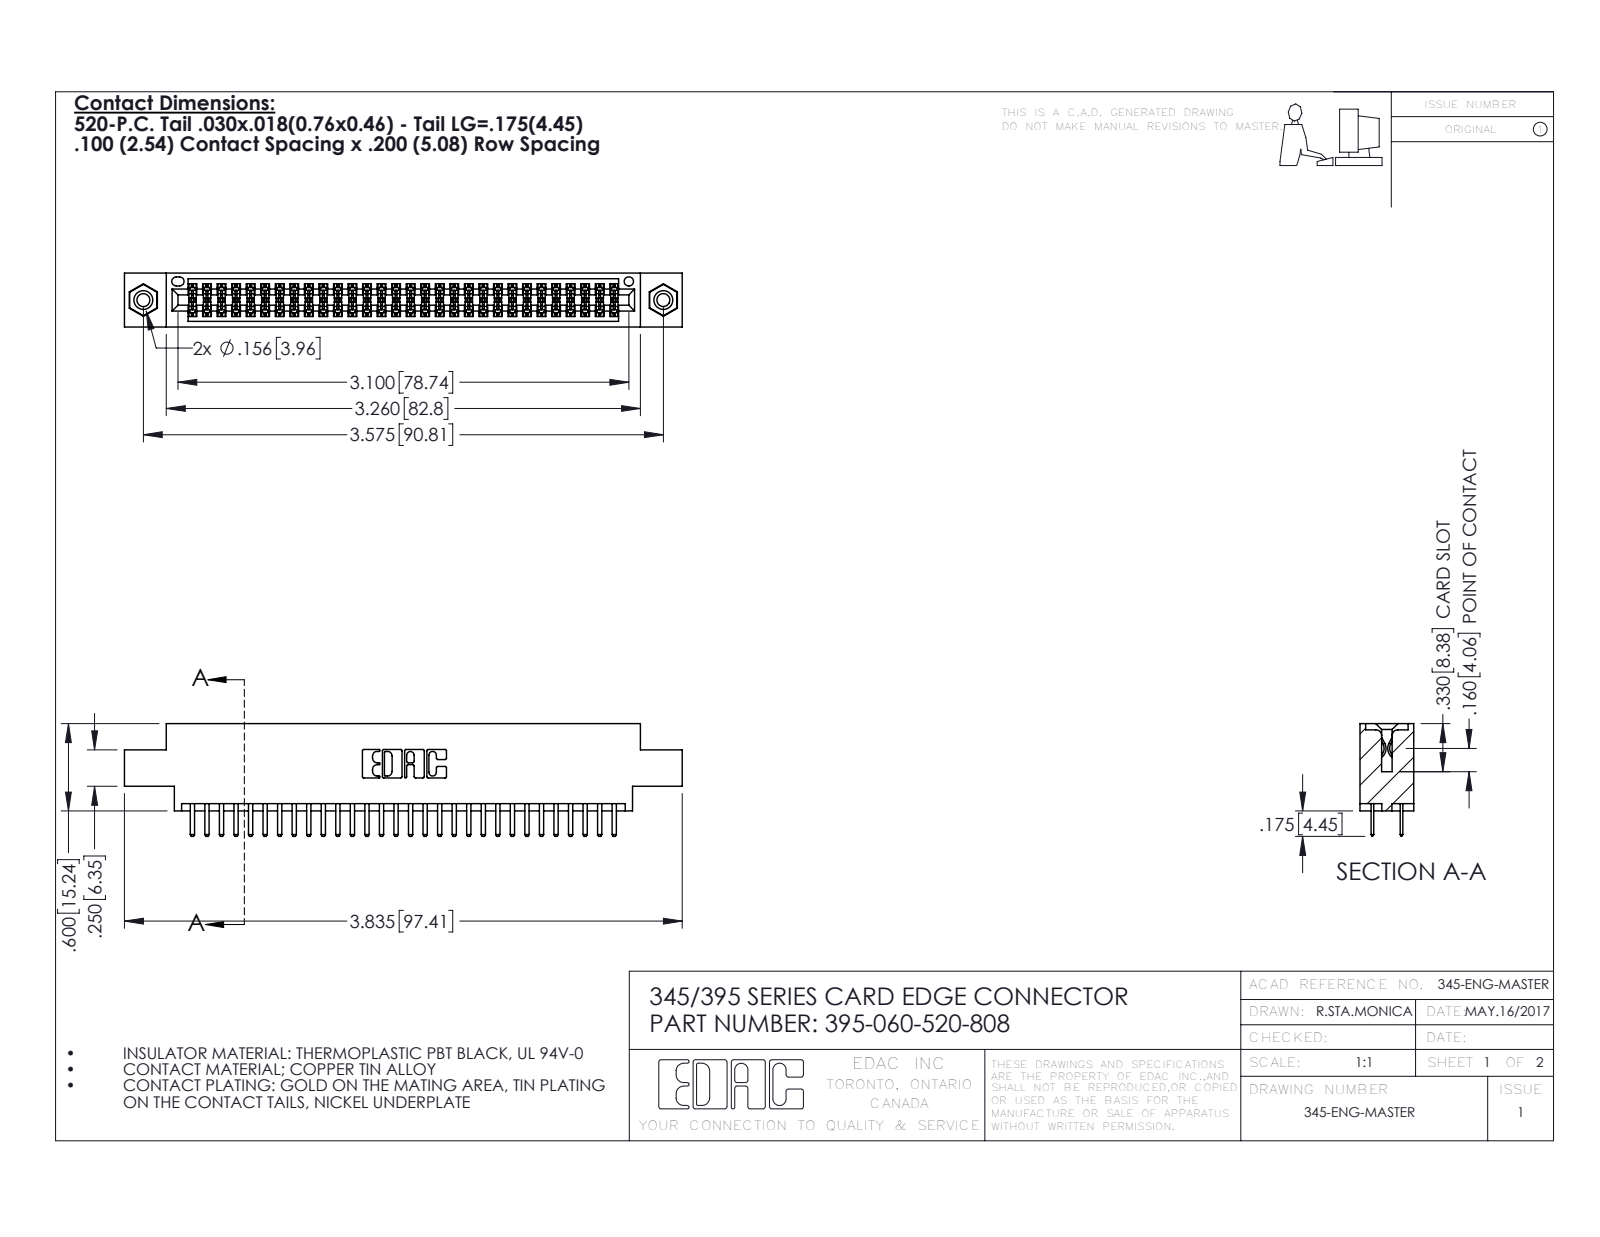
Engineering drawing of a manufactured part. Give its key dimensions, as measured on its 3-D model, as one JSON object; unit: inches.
{"part_name": "395-060-520-808; 345-292-001_345-293-120; 345-250-001_345-250-003-102; 345 Part_0.170 Offset - 0.156 Dia-TI", "step_written_by": "SolidWorks 2016 (CONFIG_CONTROL_DESIGN)", "units": "inches", "bodies": {"solids": 63, "faces": 3430, "planar": 2216, "cylindrical": 1198, "other": 16}, "overall_size": [3.835, 0.775, 0.37], "volume_in3": 0.562, "surface_area_in2": 20.89, "round_holes": [[0.089, 2], [0.125, 2], [0.156, 2], [0.064, 1]], "round_bosses_or_shafts": [[0.155, 2]], "partial_cylinders_radius": [[0.006, 90], [0.01, 64], [0.01, 22], [0.007, 6], [0.031, 6], [0.026, 3], [0.014, 2], [0.019, 2]], "face_to_face_distances": [0.072, 0.298, 0.2, 0.37, 0.098, 0.272, 0.025, 0.225, 0.022, 0.175], "hole_center_spacings": [0.27, 3.34, 3.575]}
